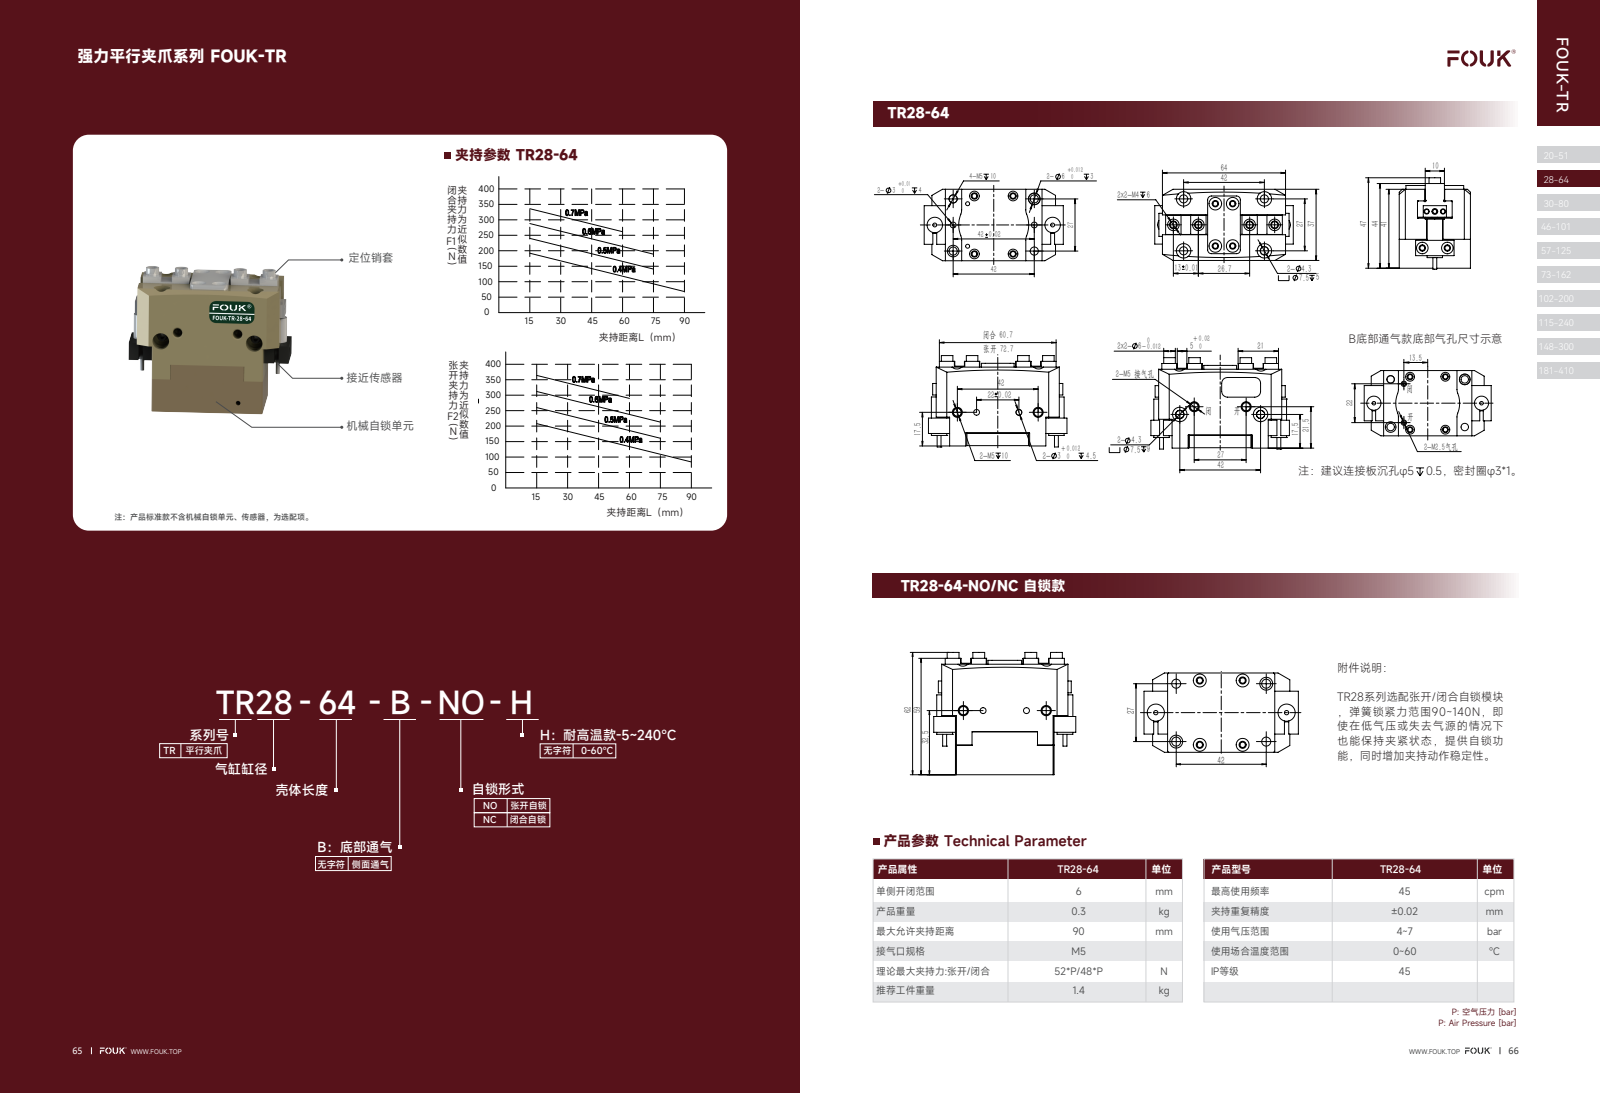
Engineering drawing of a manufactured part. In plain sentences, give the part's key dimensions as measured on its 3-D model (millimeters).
The part is named "TR28-64; 20x10-R3". Its 3-D file was written by "SolidWorks 2018 (CONFIG_CONTROL_DESIGN)". It is 20 solids with 1094 faces: 543 planar, 296 cylindrical and 255 other. Overall it measures 72 by 50.5 by 37 millimeters. Its volume is 86 060 cubic millimeters and its surface area 35 491 square millimeters. Round holes: 9 of diameter 3.3, 8 of diameter 4.2, 8 of diameter 6, 6 of diameter 2.5, 6 of diameter 4.3, 6 of diameter 7.5, 5 of diameter 3, 5 of diameter 4, 2 of diameter 2, 2 of diameter 2.05, 2 of diameter 2.1, 2 of diameter 2.7. Round bosses or shafts: 4 of diameter 2, 2 of diameter 3.8, 1 of diameter 8, 1 of diameter 2.6, 1 of diameter 1.8. Partial cylindrical surfaces (rounded edges, fillets, slot ends): 18 of radius 0.12, 12 of radius 0.12, 9 of radius 0.3, 8 of radius 3, 4 of radius 2, 4 of radius 5.9, 4 of radius 6, 2 of radius 0.15. The main face-to-face distances are 15, 9.5, 27.5, 6.5, 37, 6.6, 18, 25.8, 19.2, 34.2. The hole center spacings are 25.62, 9, 13.5, 14.51, 15.53, 16.51, 16.69, 22.
